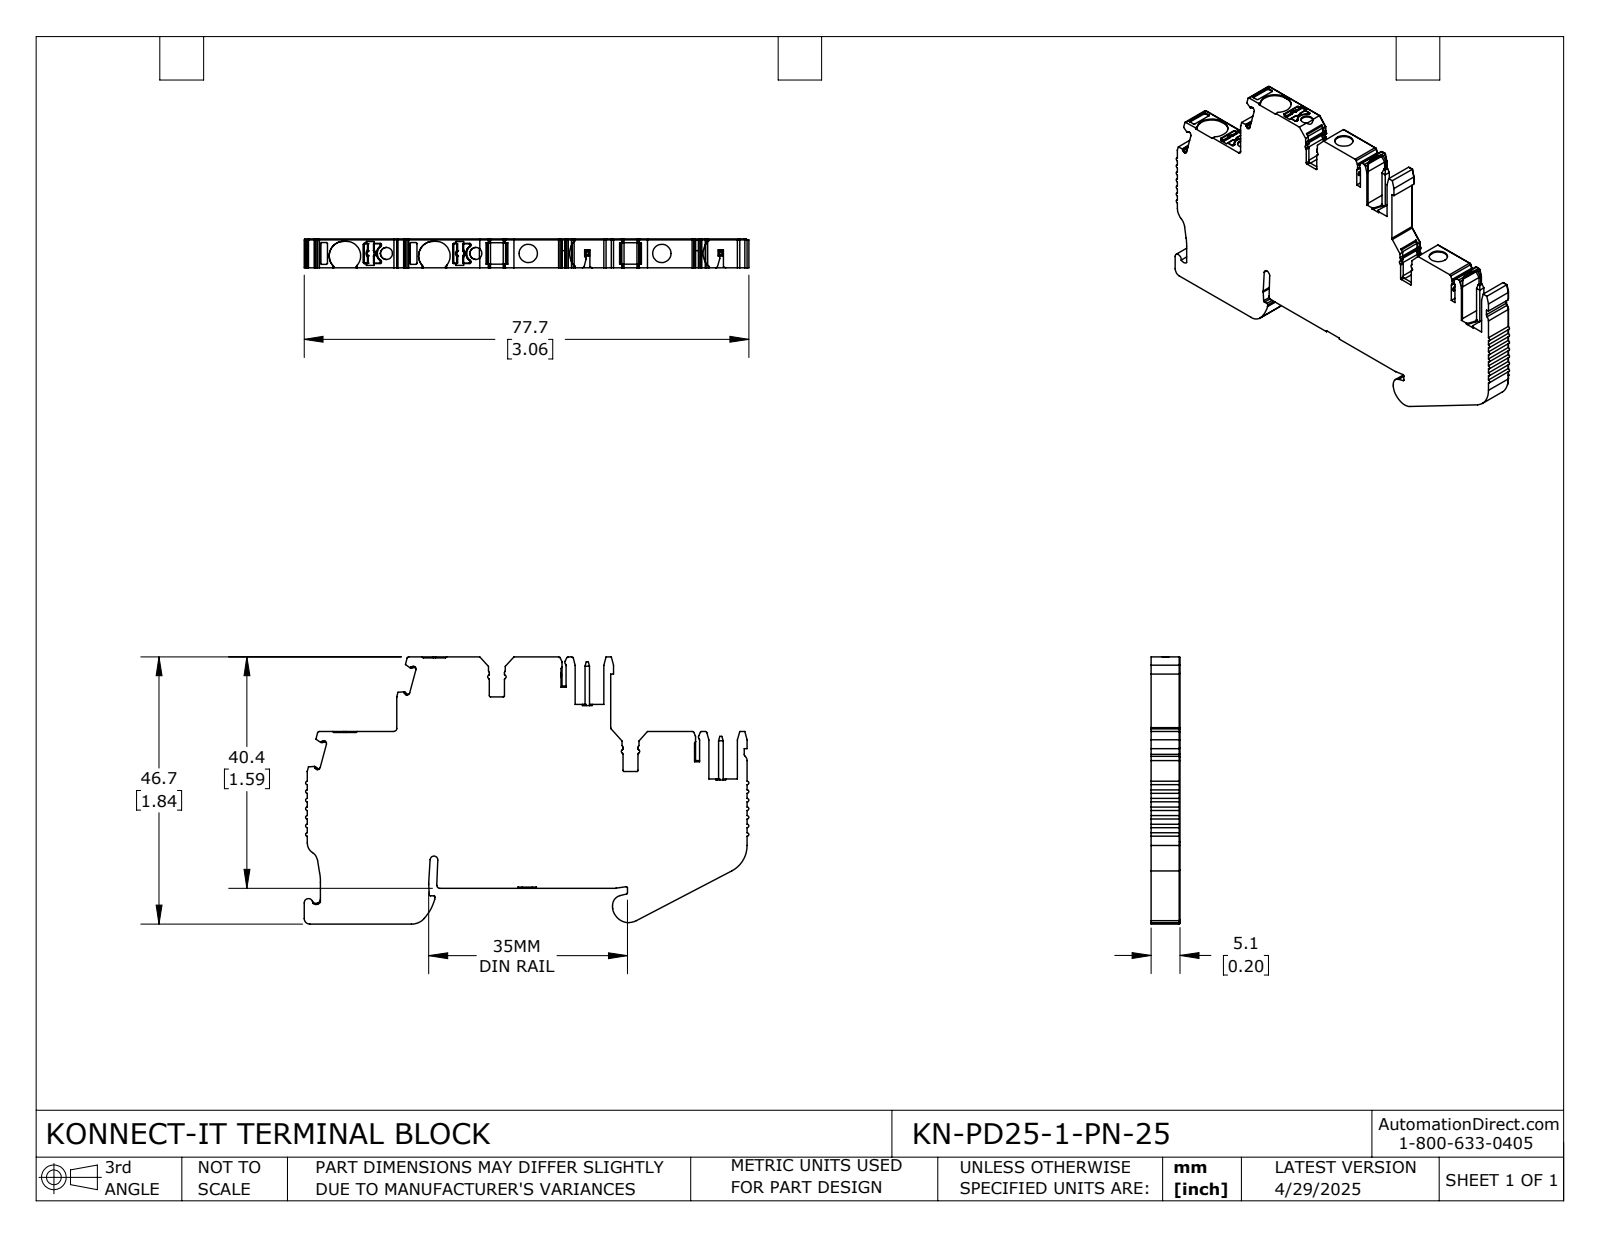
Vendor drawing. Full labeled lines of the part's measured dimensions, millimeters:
Part name (STEP PRODUCT): KN-PD25-1-PN-25
STEP written by: SolidWorks 2024 (CONFIG_CONTROL_DESIGN)
Units: millimetres
Bodies: 1 solid, 731 faces (387 planar, 304 cylindrical, 40 other)
Overall size (bounding box): 77.6 × 46.7 × 5.1
Volume: 12 900 mm³ · Surface area: 7 019 mm²
Round holes (diameter × count): ⌀2.1 ×2, ⌀3.2 ×2
Partial cylindrical surfaces — rounded edges, fillets, slot ends (radius × count): R0.2 ×58, R0.3 ×48, R0.1 ×23, R0.4 ×16, R0.5 ×16, R0.2 ×8, R0.6 ×6, R0.2 ×4
Main face-to-face distances: 5.1, 13, 23.3, 6.2, 33.6, 27.4, 46.7, 40.4, 5.2, 27.2
Hole centre spacings: 9.1, 15.6, 23.3, 24.8, 32.5, 48.1
